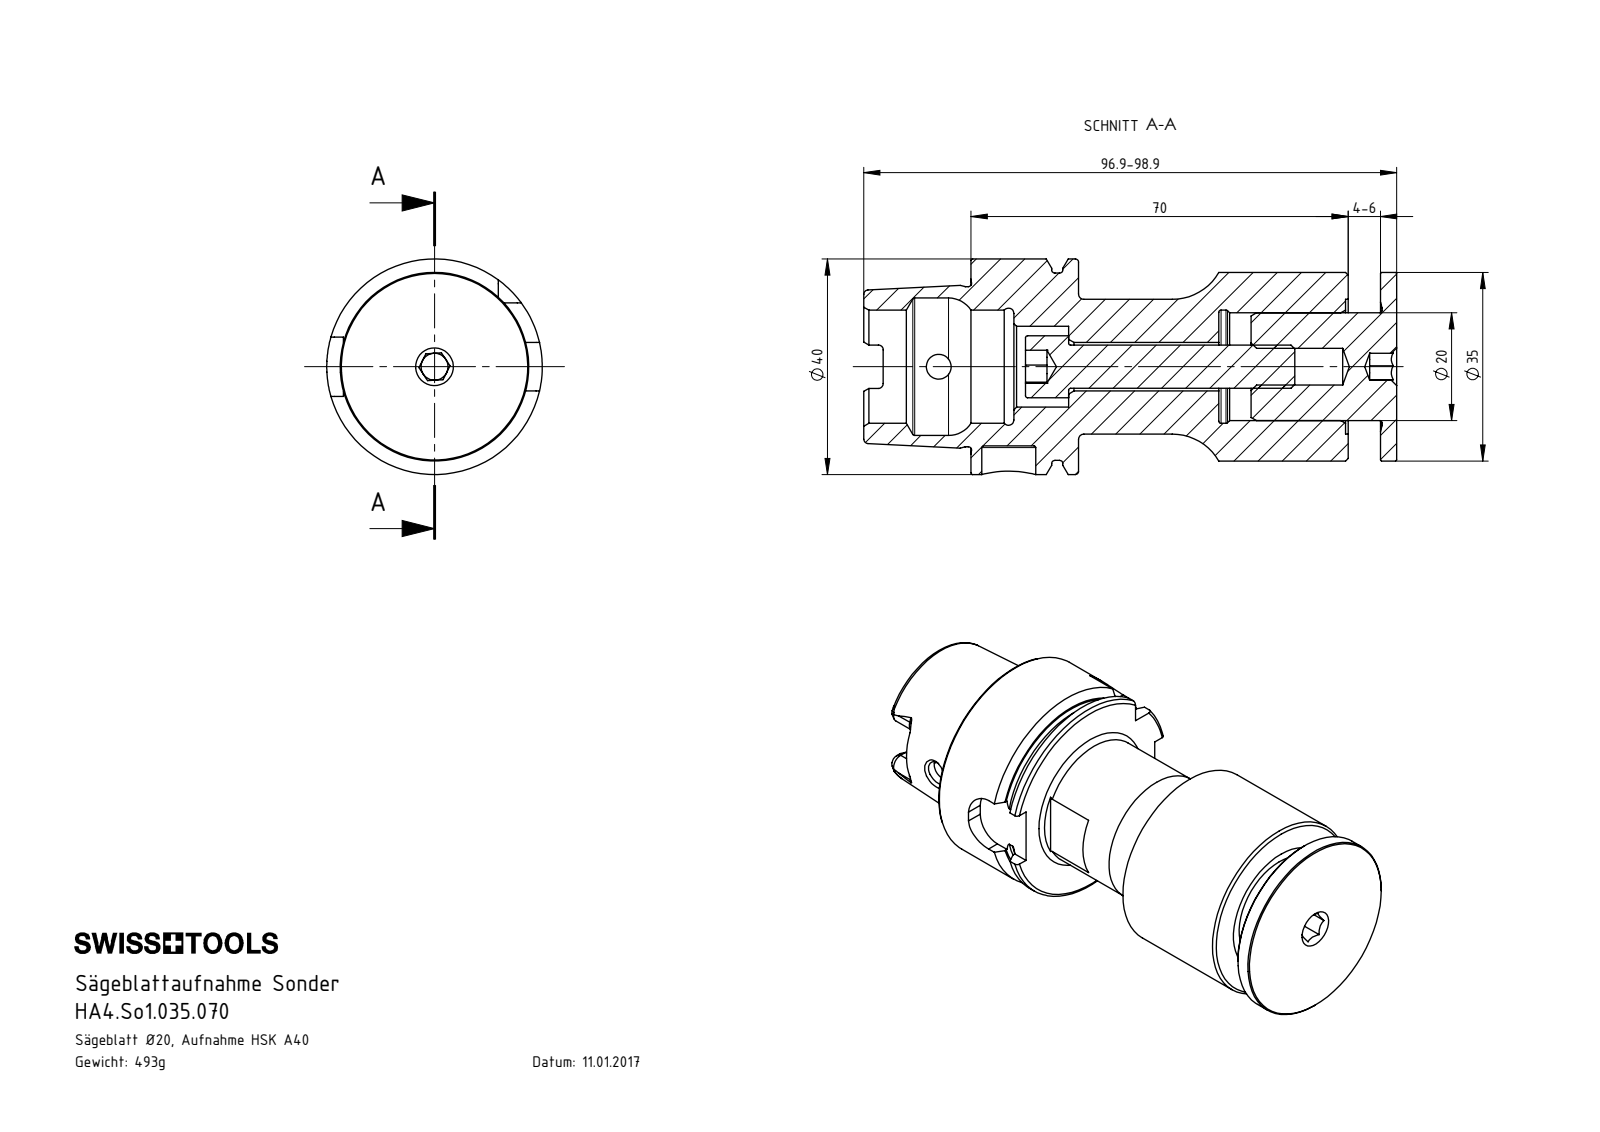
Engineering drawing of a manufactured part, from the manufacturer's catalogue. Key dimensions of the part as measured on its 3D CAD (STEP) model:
Part name (STEP PRODUCT): HA4-So1.035.070_A_Fertigbearbeitung; HA4-So1.035.070; HA4-ER1.035.070_A; ISO 4762 - M8 x 45_fr PS4-So2.035.070
STEP written by: SolidWorks 2015 (CONFIG_CONTROL_DESIGN)
Units: millimetres
Bodies: 3 solids, 247 faces (82 planar, 62 cylindrical, 103 other)
Overall size (bounding box): 98.9 × 40 × 40
Volume: 62 824 mm³ · Surface area: 23 011 mm²
Round holes (diameter × count): ⌀4.6 ×1, ⌀6.8 ×1, ⌀9 ×1, ⌀10 ×1, ⌀15 ×1, ⌀20 ×1, ⌀21 ×1, ⌀25 ×1, ⌀25.5 ×1
Round bosses / shafts (diameter × count): ⌀40 ×1, ⌀35 ×1, ⌀34.75 ×1, ⌀29.71 ×1, ⌀11.5 ×1, ⌀8 ×1
Partial cylindrical surfaces — rounded edges, fillets, slot ends (radius × count): R0.9 ×6, R1.88 ×4, R4.5 ×4
Main face-to-face distances: 6, 59.05, 56.05, 3, 24, 9, 50.05, 19.95, 70, 76
